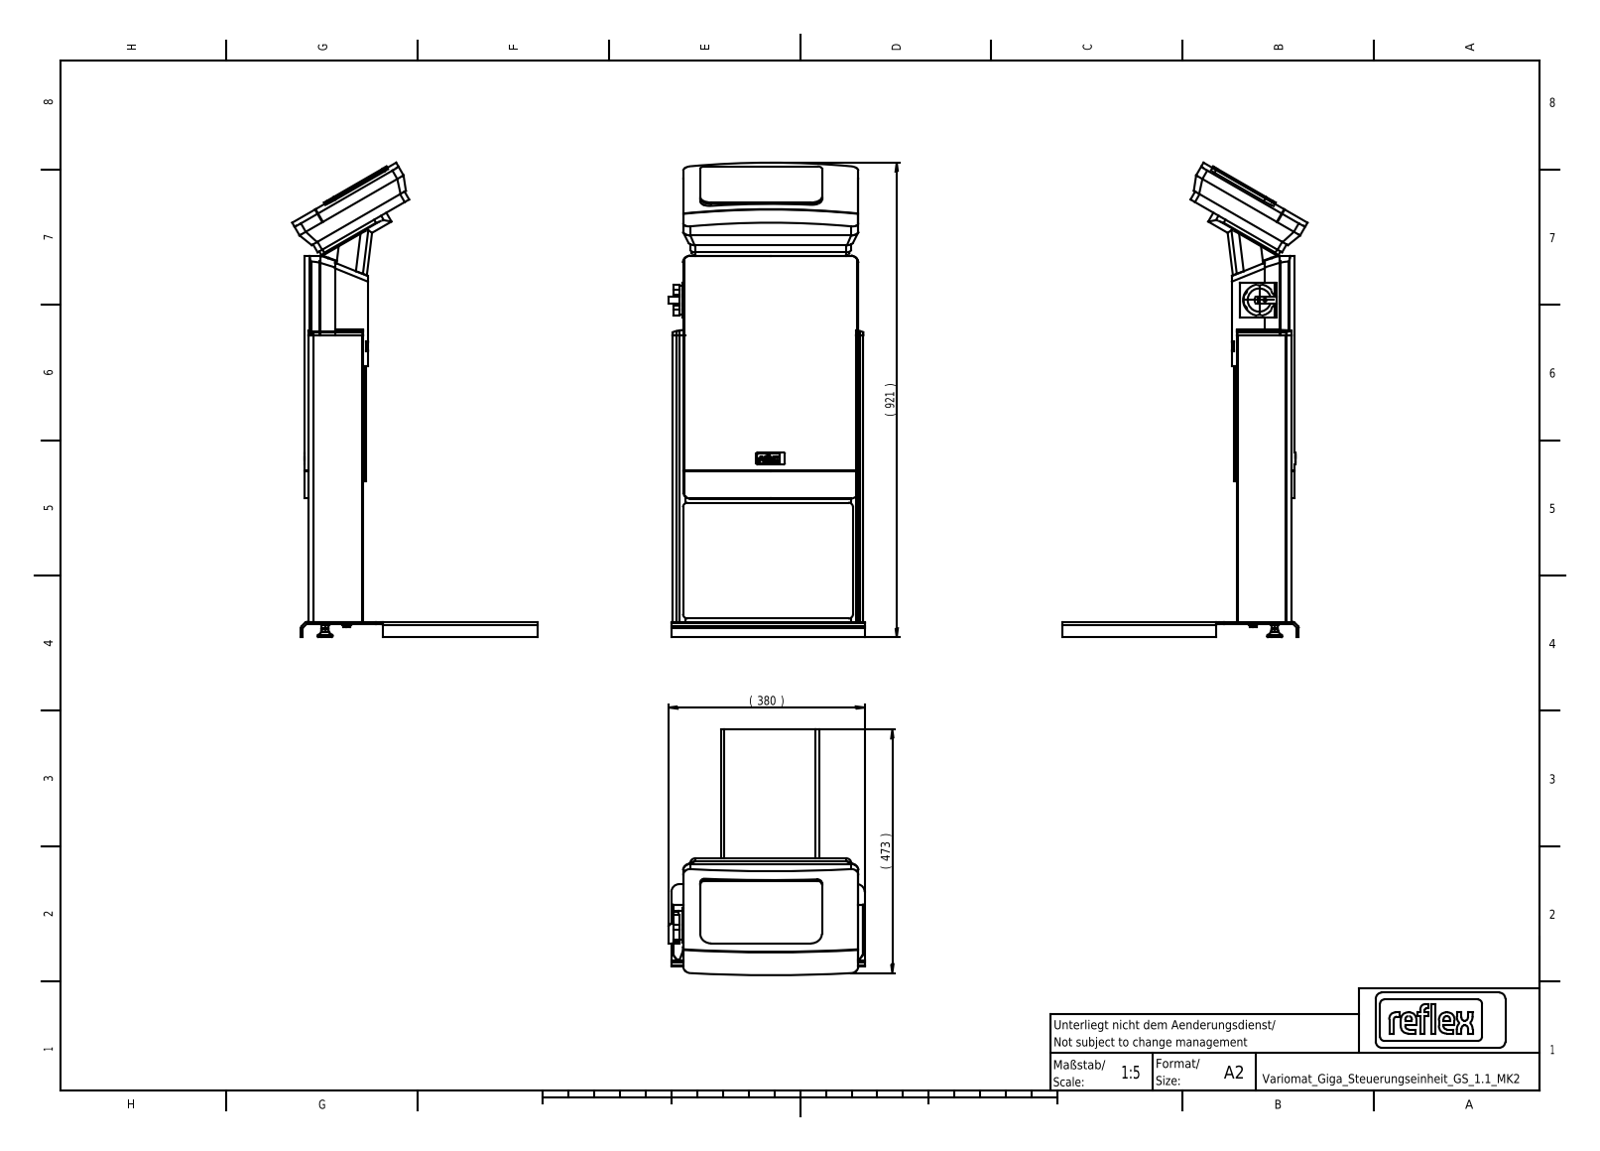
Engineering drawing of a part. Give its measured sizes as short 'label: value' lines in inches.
written by: Mechanical Desktop 2011 (CONFIG_CONTROL_DESIGN)
unit: in
bodies: 81 solids, 2282 faces (977 planar, 508 cylindrical, 797 other)
size: 36.247 × 18.767 × 14.972
volume: 1 595 in³; area: 3 343 in²
holes: 13× ⌀0.689, 8× ⌀0.413, 8× ⌀0.669, 6× ⌀0.217, 4× ⌀0.354, 4× ⌀0.531, 3× ⌀0.213, 3× ⌀0.807, 2× ⌀0.906, 1× ⌀0.244, 1× ⌀0.252, 1× ⌀0.846
bosses: 12× ⌀0.787, 12× ⌀0.63, 9× ⌀0.441, 9× ⌀0.201, 8× ⌀0.748, 8× ⌀0.689, 4× ⌀0.906, 4× ⌀0.631
rounds: 25× R0.118, 8× R0.394, 6× R0.295, 6× R0.551, 5× R0.039, 4× R0.044, 4× R0.066, 4× R0.069
face distances: 0.394, 4.016, 3.622, 13.623, 2.933, 2.933, 0.157, 0.079, 12.678, 0.945
hole spacings: 1.22, 2.441, 1.417, 3.661, 2.835, 4.882, 0.063, 4.677
